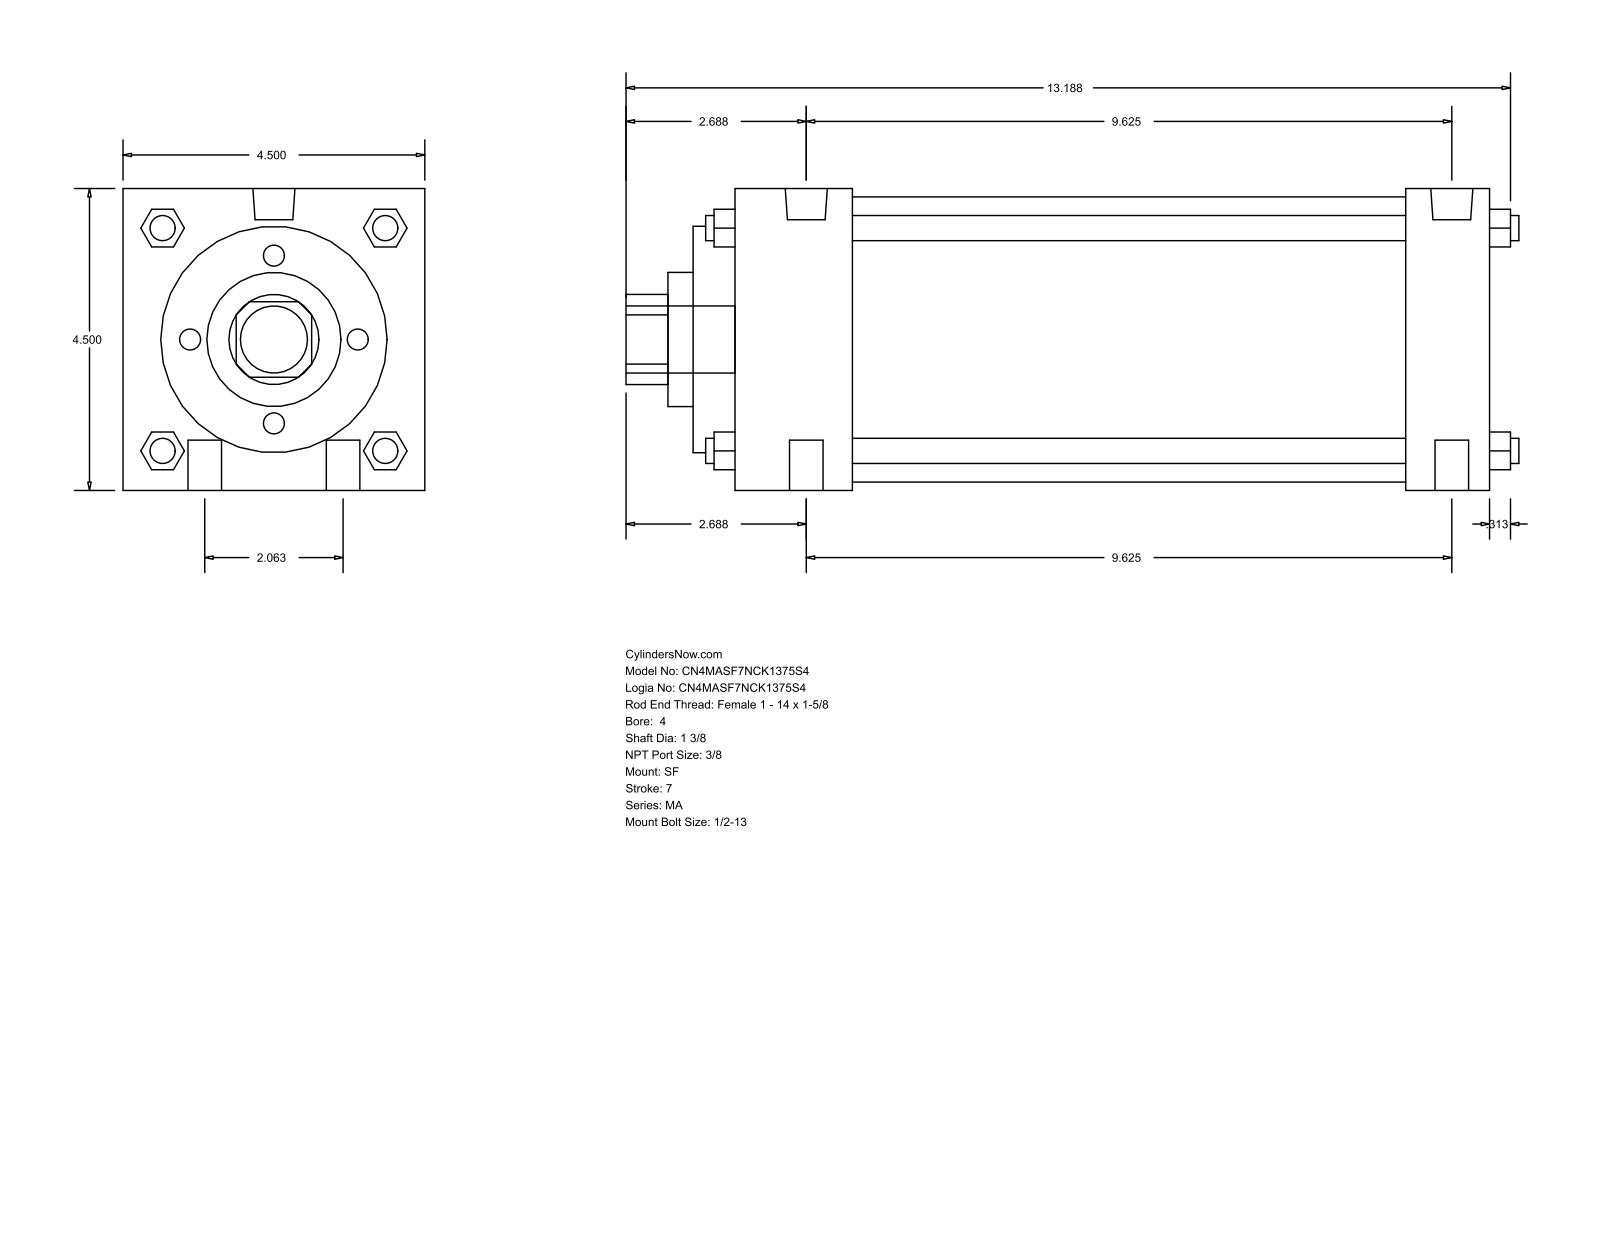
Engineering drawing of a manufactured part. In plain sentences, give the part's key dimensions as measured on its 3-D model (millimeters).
The part is named "MA_SF__0400_1.375". Its 3-D file was written by "GSSL Pune (CONFIG_CONTROL_DESIGN)". It is 0 solids with 126 faces: 95 planar, 31 cylindrical and 0 other. Overall it measures 338.14 by 114.3 by 114.3 millimeters. Round holes: 1 of diameter 34.92, 1 of diameter 50.8, 1 of diameter 85.72, 1 of diameter 107.95. Round bosses or shafts: 4 of diameter 12.7, 4 of diameter 9.53, 2 of diameter 15.93, 2 of diameter 11.11, 1 of diameter 25.4. Partial cylindrical surfaces (rounded edges, fillets, slot ends): 1 of radius 17.06. The main face-to-face distances are 114.3, 285.75, 301.62, 15.87, 269.87, 254, 31.75, 60.32, 44.45, 209.55.
